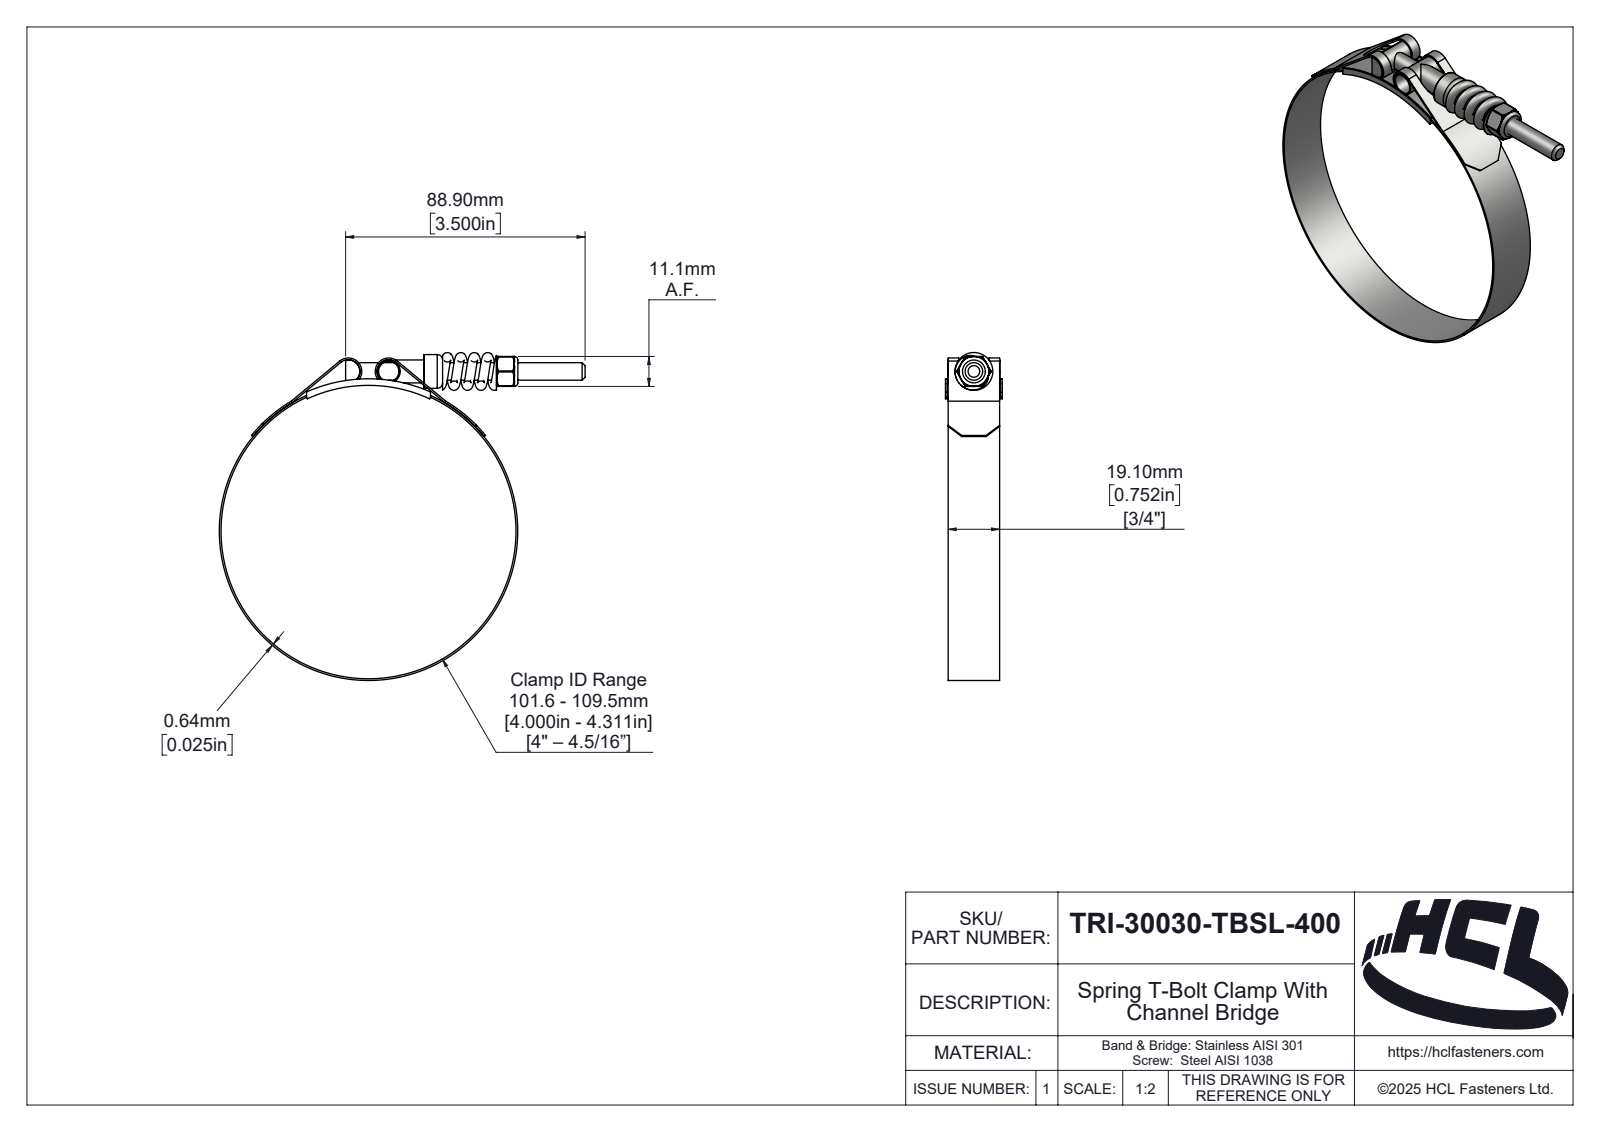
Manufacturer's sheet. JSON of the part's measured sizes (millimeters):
{"part_name": "TRI-30030-TBSL-400", "step_written_by": "SolidWorks 2025 (AUTOMOTIVE_DESIGN)", "units": "millimeters", "bodies": {"solids": 7, "faces": 332, "planar": 48, "cylindrical": 122, "other": 162}, "overall_size": [136.79, 121.69, 21.1], "volume_mm3": 12335, "surface_area_mm2": 25782, "round_holes": [[5.4, 1], [6.35, 1], [6.5, 1], [7.52, 1], [109.5, 1]], "round_bosses_or_shafts": [[8.52, 2], [110.78, 1], [12.52, 1]], "partial_cylinders_radius": [[0.39, 6], [0.5, 2], [4.36, 2], [5, 2], [54.11, 2], [0.59, 1], [2.42, 1], [3.03, 1]], "face_to_face_distances": [0.64, 19.1, 1, 20.1, 20.46, 0.36, 19.46, 56, 21.1, 11.11], "hole_center_spacings": [59.75]}
